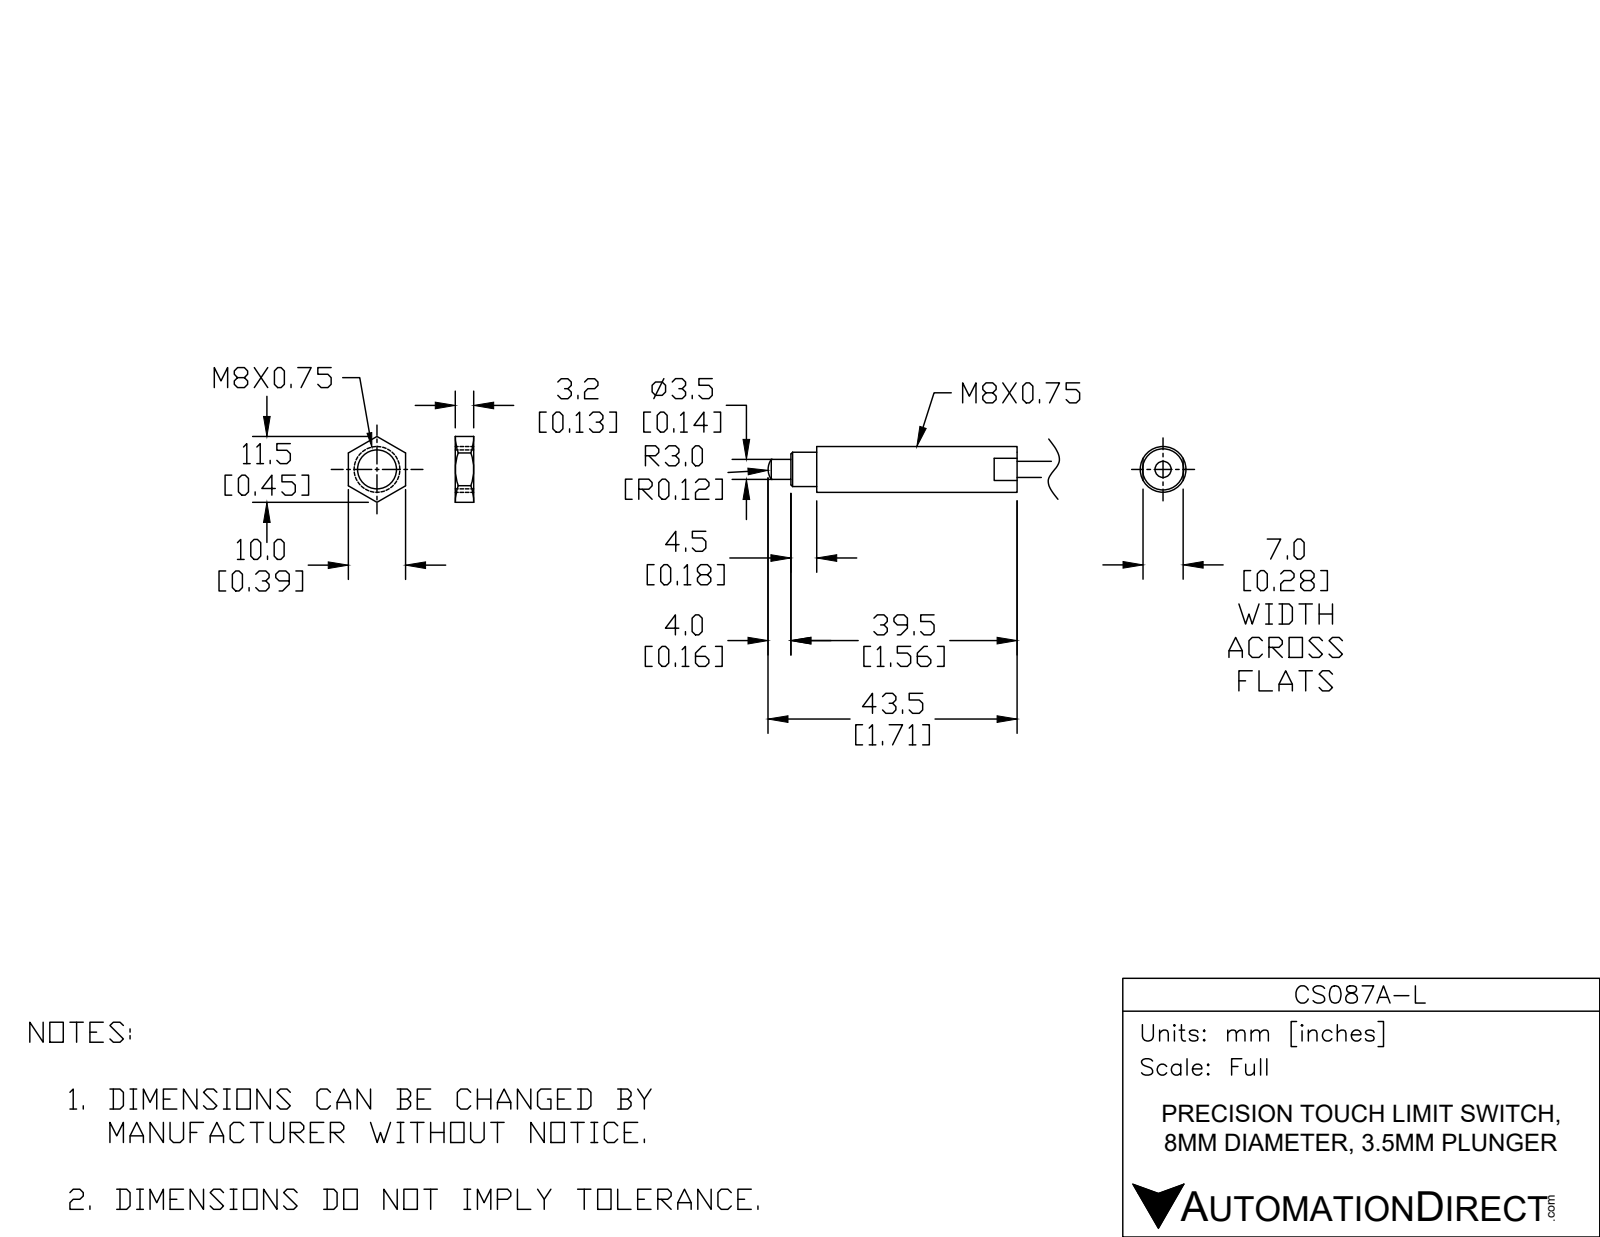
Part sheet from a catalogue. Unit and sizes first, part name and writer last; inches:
Units: inches
Overall size (bounding box): 1.949 × 0.314 × 0.314
Round bosses / shafts (diameter × count): ⌀0.314 ×1, ⌀0.236 ×1, ⌀0.138 ×1, ⌀0.11 ×1
Main face-to-face distances: 0.275, 1.378, 0.177, 1.555, 1.791, 1.614, 0.236, 1.386, 1.209, 0.169
Volume: 0.118 in³ · Surface area: 1.77 in²
Bodies: 1 solid, 24 faces (8 planar, 8 cylindrical, 8 other)
Part name (STEP PRODUCT): CS087A-L
STEP written by: SolidWorks 2017 (AUTOMOTIVE_DESIGN)
